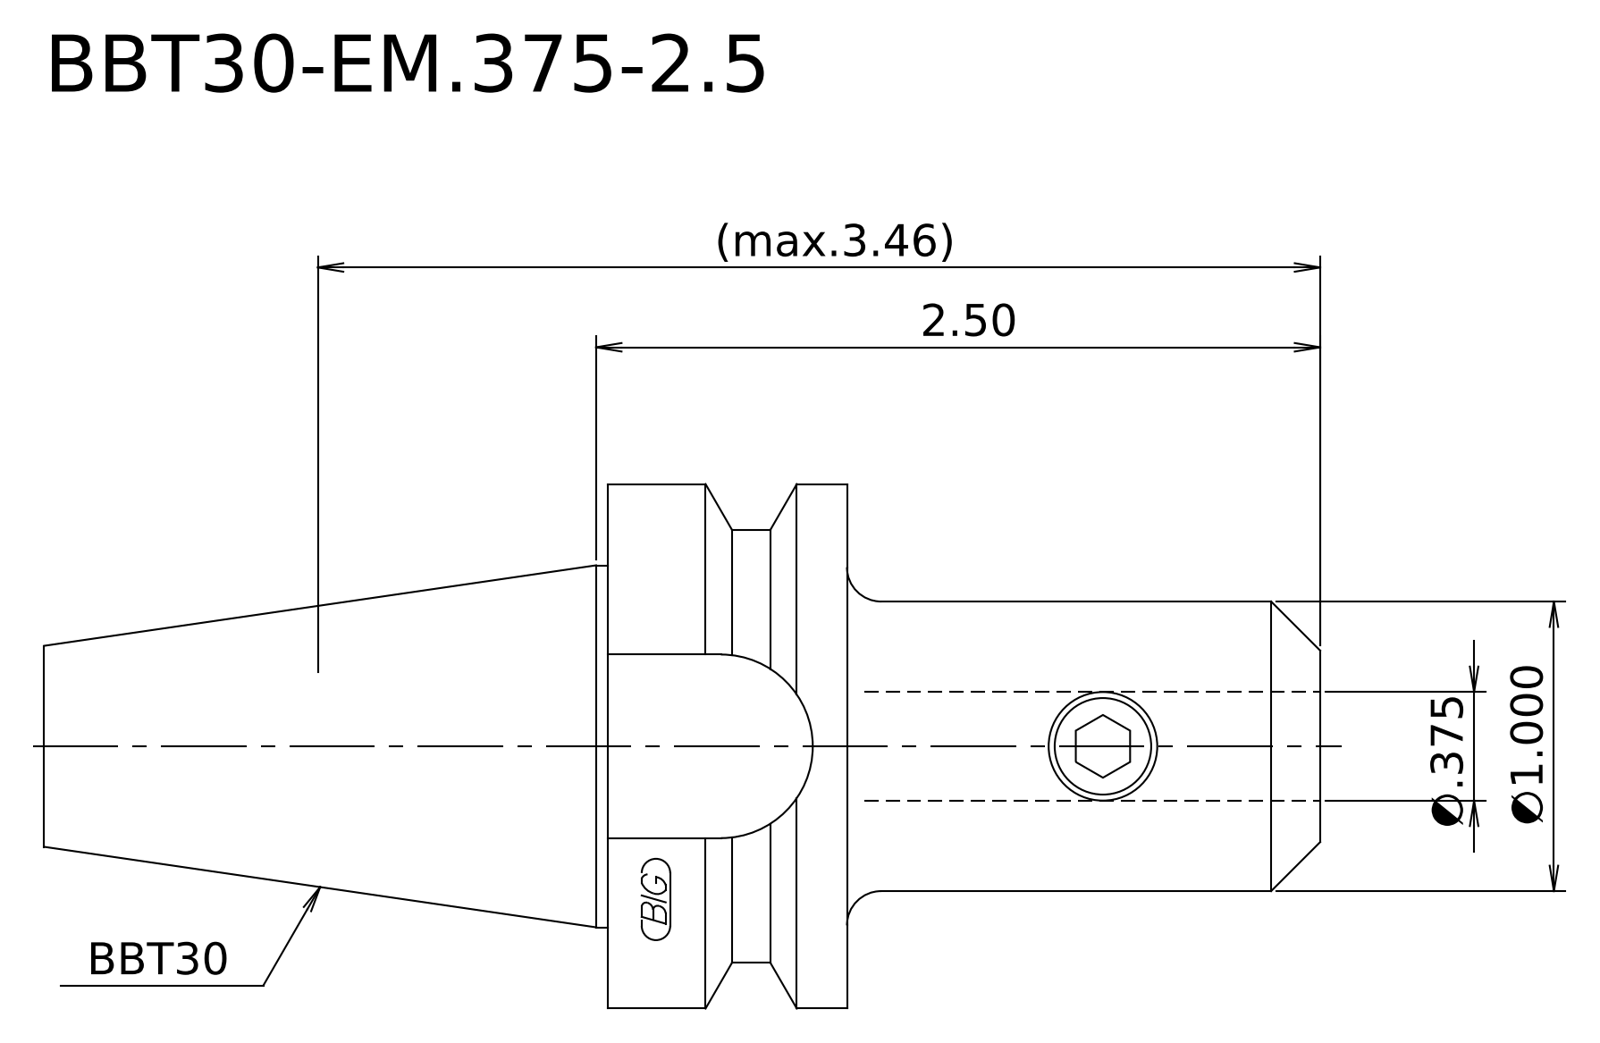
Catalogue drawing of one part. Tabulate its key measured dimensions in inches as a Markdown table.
| quantity | value |
| --- | --- |
| STEP written by | Kubotek KeyCreator 2011 V10.0.2 (22737) (automotive_design) |
| units | inches |
| bodies | 1 solid, 14 faces (4 planar, 5 cylindrical, 5 other) |
| overall size | 4.406 × 1.811 × 1.811 |
| volume | 4.712 in³ |
| surface area | 20.35 in² |
| round bosses / shafts (diameter × count) | 1.811 × 1, 1.496 × 1, 1.25 × 1, 1 × 1 |
| main face-to-face distances | 0.827, 2.772, 1.945, 1.634, 2.461, 4.406 |
